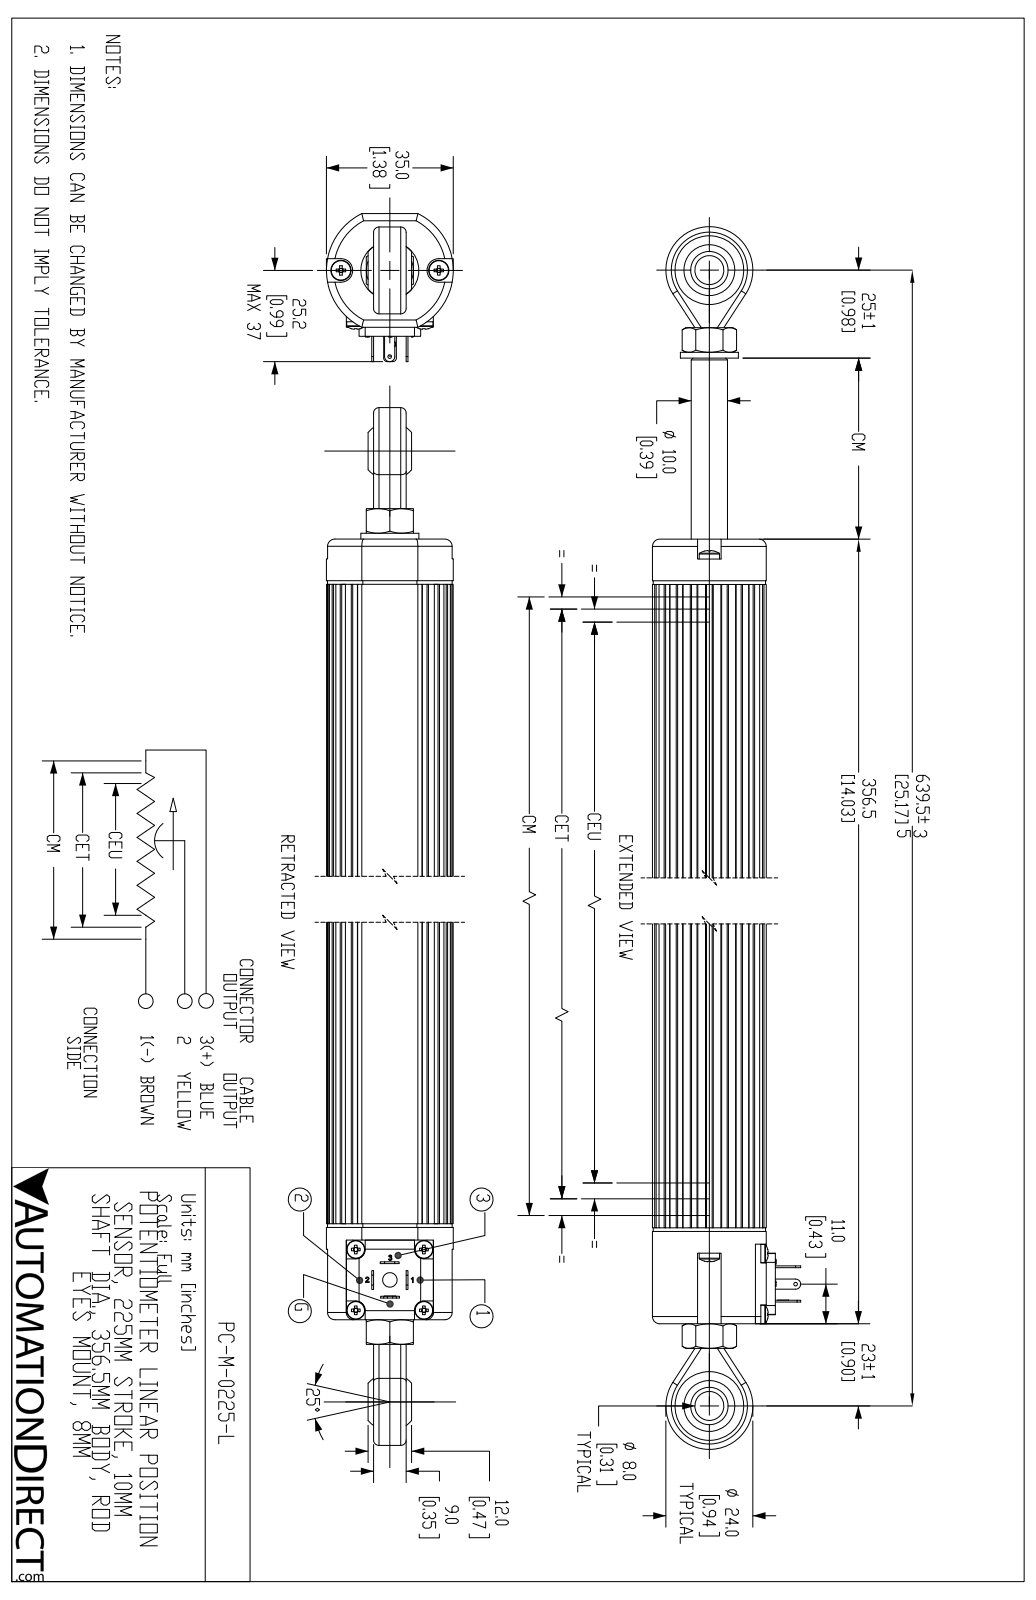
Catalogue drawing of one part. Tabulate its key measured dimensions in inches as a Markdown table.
| quantity | value |
| --- | --- |
| part name | PC-M-0225-L |
| STEP written by | SolidWorks 2019 (AUTOMOTIVE_DESIGN) |
| units | inches |
| bodies | 26 solids, 1441 faces (437 planar, 366 cylindrical, 638 other) |
| overall size | 17.072 × 1.61 × 1.378 |
| volume | 21.95 in³ |
| surface area | 121.3 in² |
| round holes (diameter × count) | 0.087 × 4, 0.102 × 4, 0.039 × 3, 0.108 × 2, 0.138 × 2, 0.315 × 2, 0.748 × 2, 0.114 × 1, 0.157 × 1, 0.268 × 1, 0.331 × 1, 0.512 × 1 |
| round bosses / shafts (diameter × count) | 0.197 × 4, 0.098 × 4, 0.118 × 3, 0.22 × 2, 0.63 × 1, 0.394 × 1, 0.39 × 1, 0.315 × 1 |
| partial cylindrical surfaces (radius × count) | 0.059 × 8, 0.039 × 5, 0.079 × 5, 0.102 × 4, 0.118 × 4, 0.055 × 2, 0.128 × 2, 0.472 × 2 |
| main face-to-face distances | 1.236, 0.039, 12.539, 12.5, 0.913, 12.579, 0.913, 0.118, 1.118, 13.583 |
| hole center spacings | 0.496, 0.531, 0.661, 0.74, 0.993, 0.024, 0.11, 0.134 |
